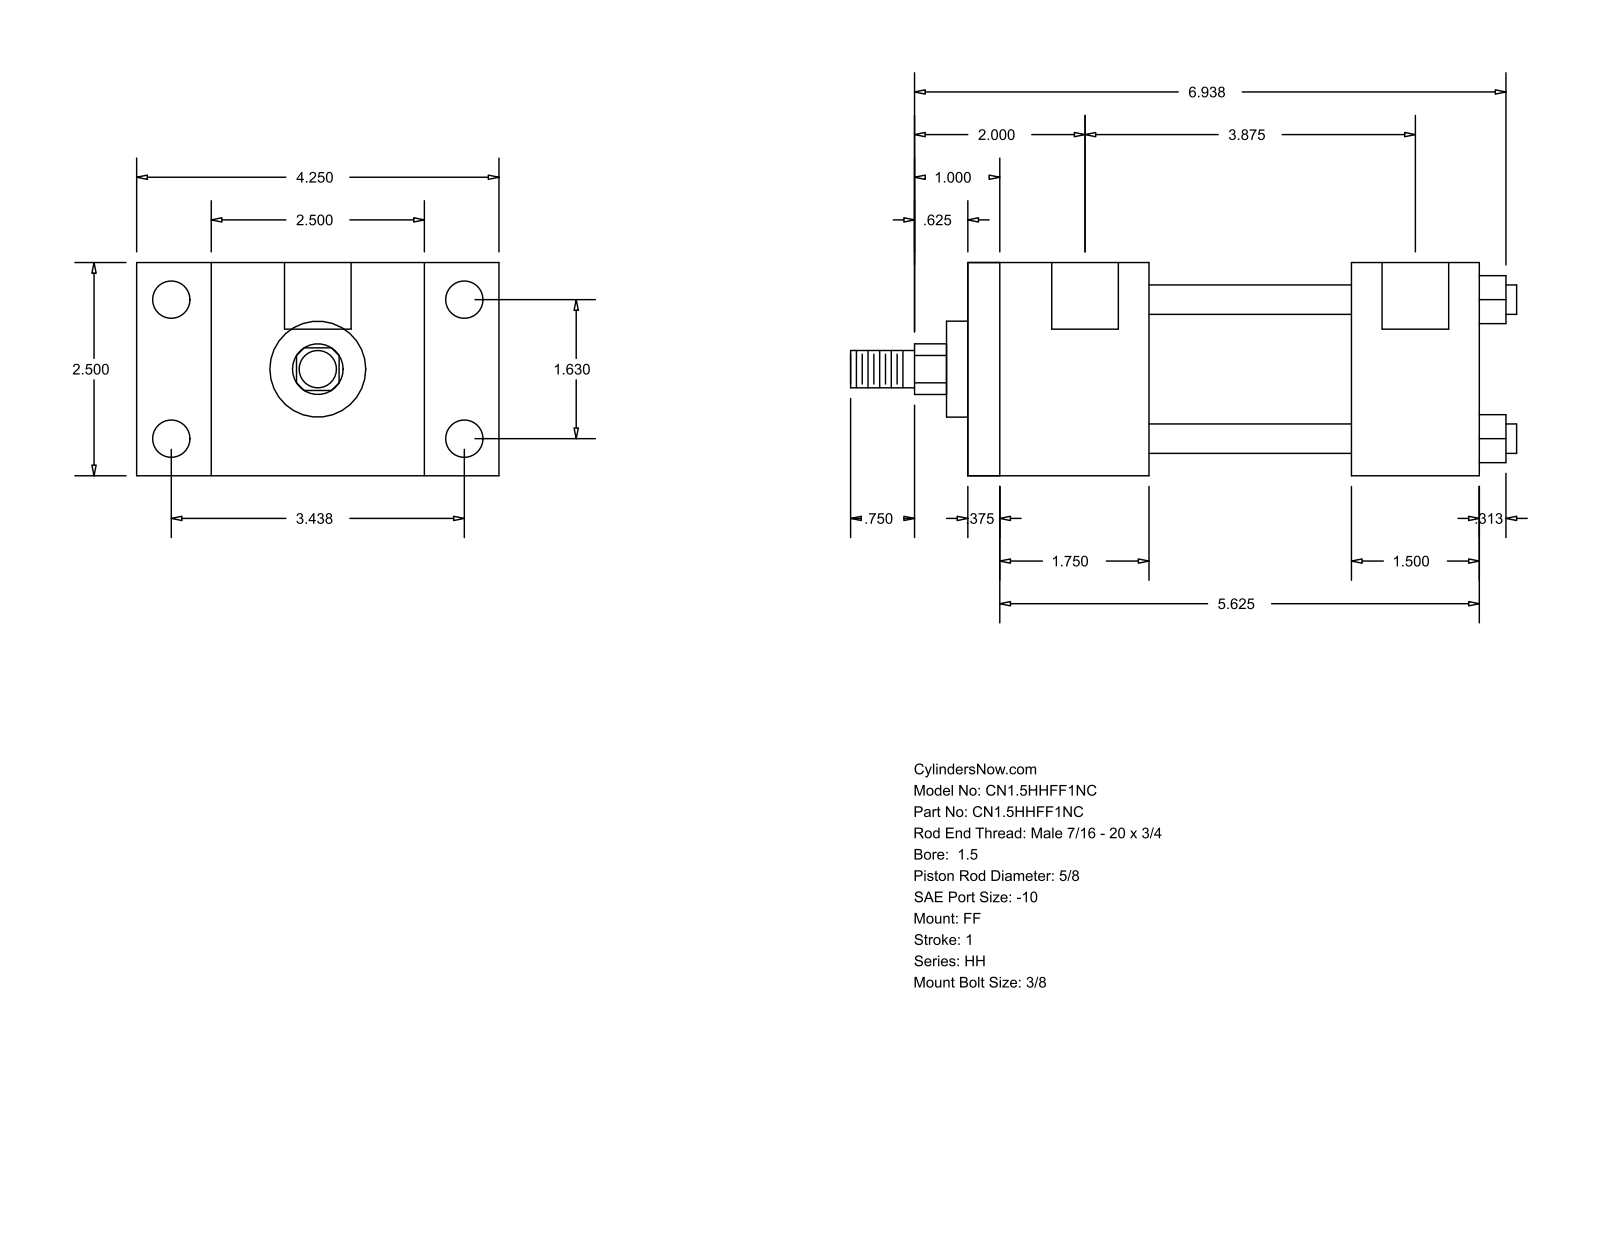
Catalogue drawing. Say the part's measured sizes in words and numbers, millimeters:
The part is named "HH_FF__0150_0.625". Its 3-D file was written by "GSSL Pune (CONFIG_CONTROL_DESIGN)". It is 0 solids with 92 faces: 64 planar, 28 cylindrical and 0 other. Overall it measures 198.44 by 107.95 by 63.5 millimeters. Round holes: 4 of diameter 5.56, 4 of diameter 11.13, 2 of diameter 19.84. Round bosses or shafts: 4 of diameter 8.76, 1 of diameter 44.45, 1 of diameter 28.57, 1 of diameter 15.88, 1 of diameter 11.11. Partial cylindrical surfaces (rounded edges, fillets, slot ends): 1 of radius 7.54. The main face-to-face distances are 63.5, 152.4, 38.1, 9.52, 142.88, 60.33, 44.45, 53.97, 98.43, 114.3. The hole center spacings are 1.59, 41.4, 87.32, 96.64, 100.01, 101.6, 98.42.
